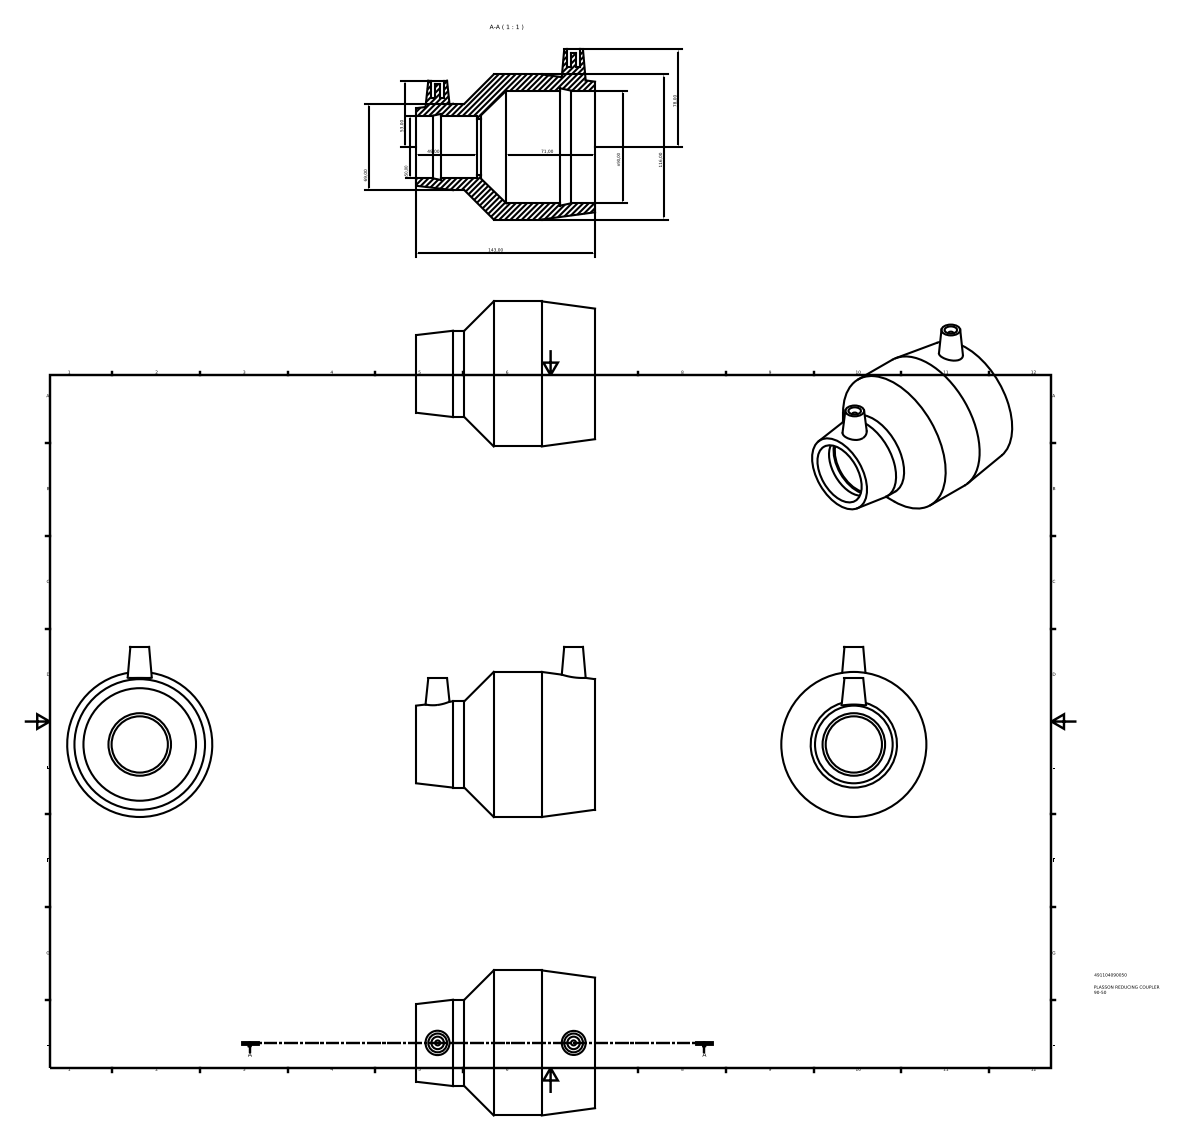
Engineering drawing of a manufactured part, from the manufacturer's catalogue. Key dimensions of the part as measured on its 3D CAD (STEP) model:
Part name (STEP PRODUCT): 491104090050
STEP written by: Autodesk Inventor 2015 (AUTOMOTIVE_DESIGN)
Units: millimetres
Bodies: 1 solid, 31 faces (12 planar, 11 cylindrical, 8 other)
Overall size (bounding box): 143 × 136 × 116
Volume: 479 086 mm³ · Surface area: 89 349 mm²
Round holes (diameter × count): ⌀10 ×2, ⌀45 ×1, ⌀50 ×1, ⌀90 ×1
Round bosses / shafts (diameter × count): ⌀4 ×2, ⌀116 ×1, ⌀69 ×1
Main face-to-face distances: 143, 114.6, 28.4, 51.45, 63.15, 91.55, 49, 2.45, 65.6, 94
Hole centre spacings: 108.68
